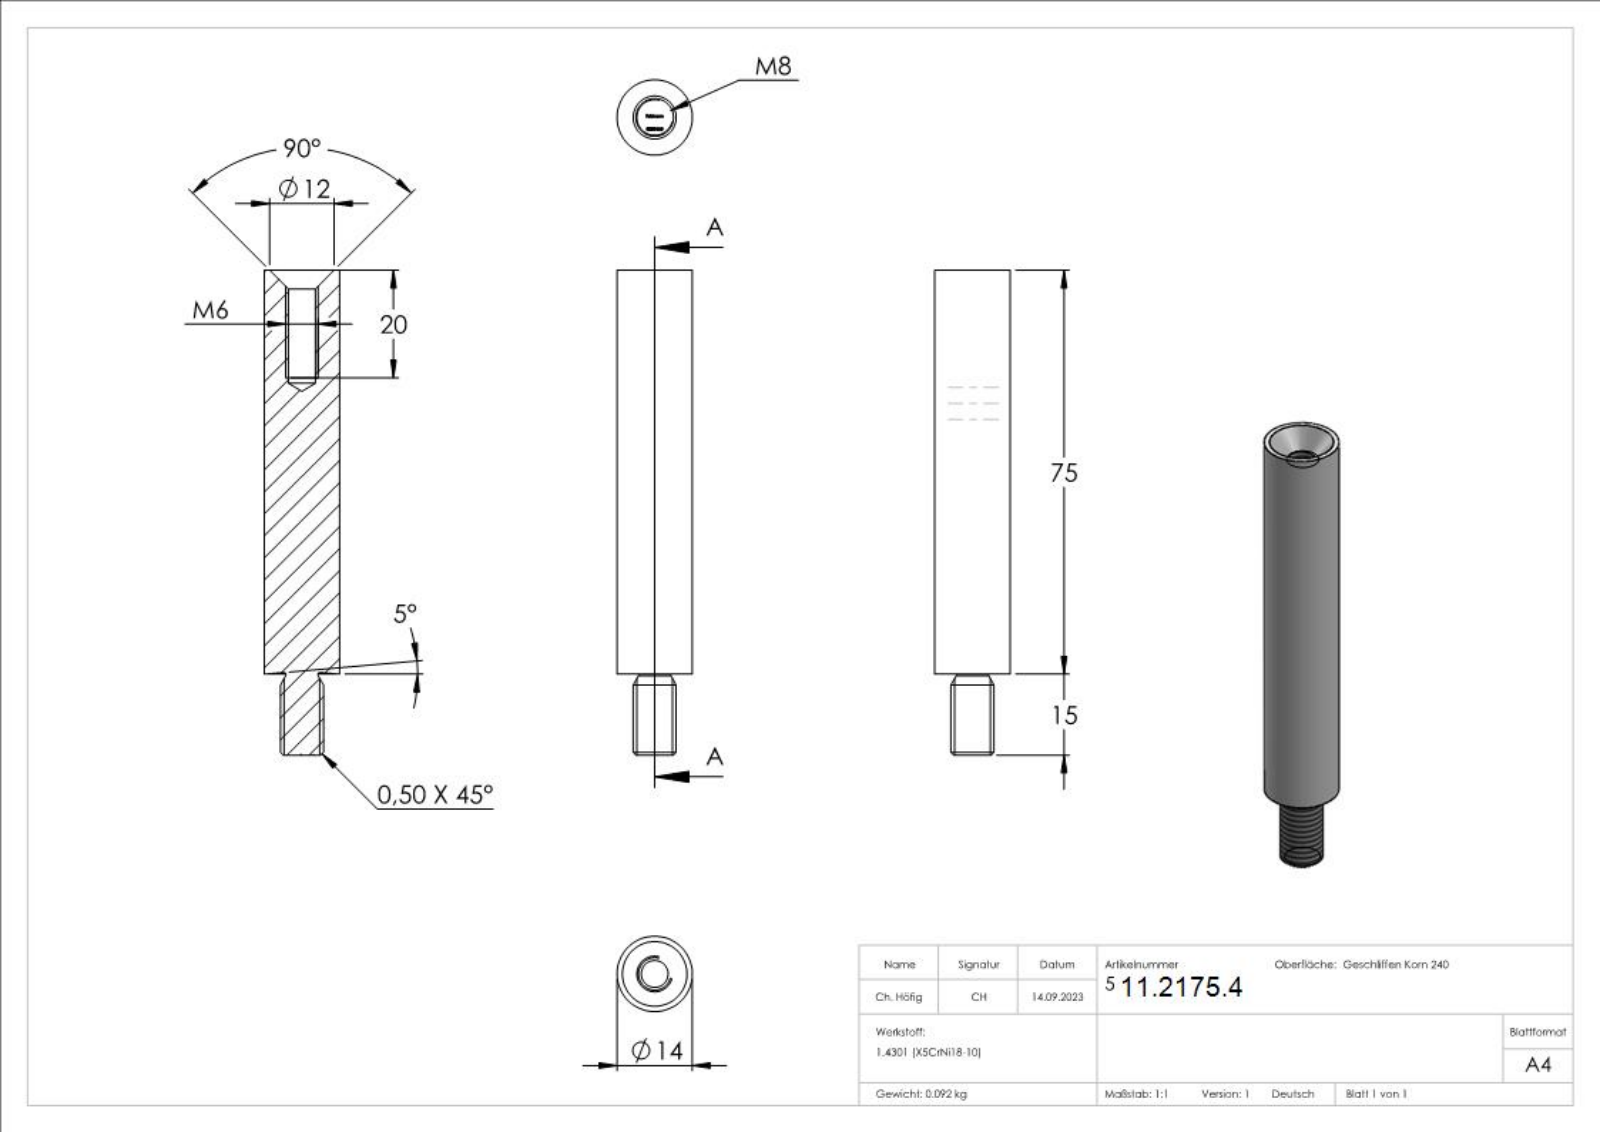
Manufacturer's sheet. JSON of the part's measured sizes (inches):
{"part_name": "50233-240", "step_written_by": "SolidWorks 2018 (CONFIG_CONTROL_DESIGN)", "units": "inches", "bodies": {"solids": 1, "faces": 269, "planar": 157, "cylindrical": 3, "other": 109}, "overall_size": [3.543, 0.551, 0.551], "volume_in3": 0.713, "surface_area_in2": 6.699, "round_holes": [[0.197, 1]], "round_bosses_or_shafts": [[0.551, 1], [0.315, 1]], "face_to_face_distances": [3.543, 3.539, 0.03, 0.051, 0.094, 0.094, 0.028, 0.061, 0.096, 0.022]}
